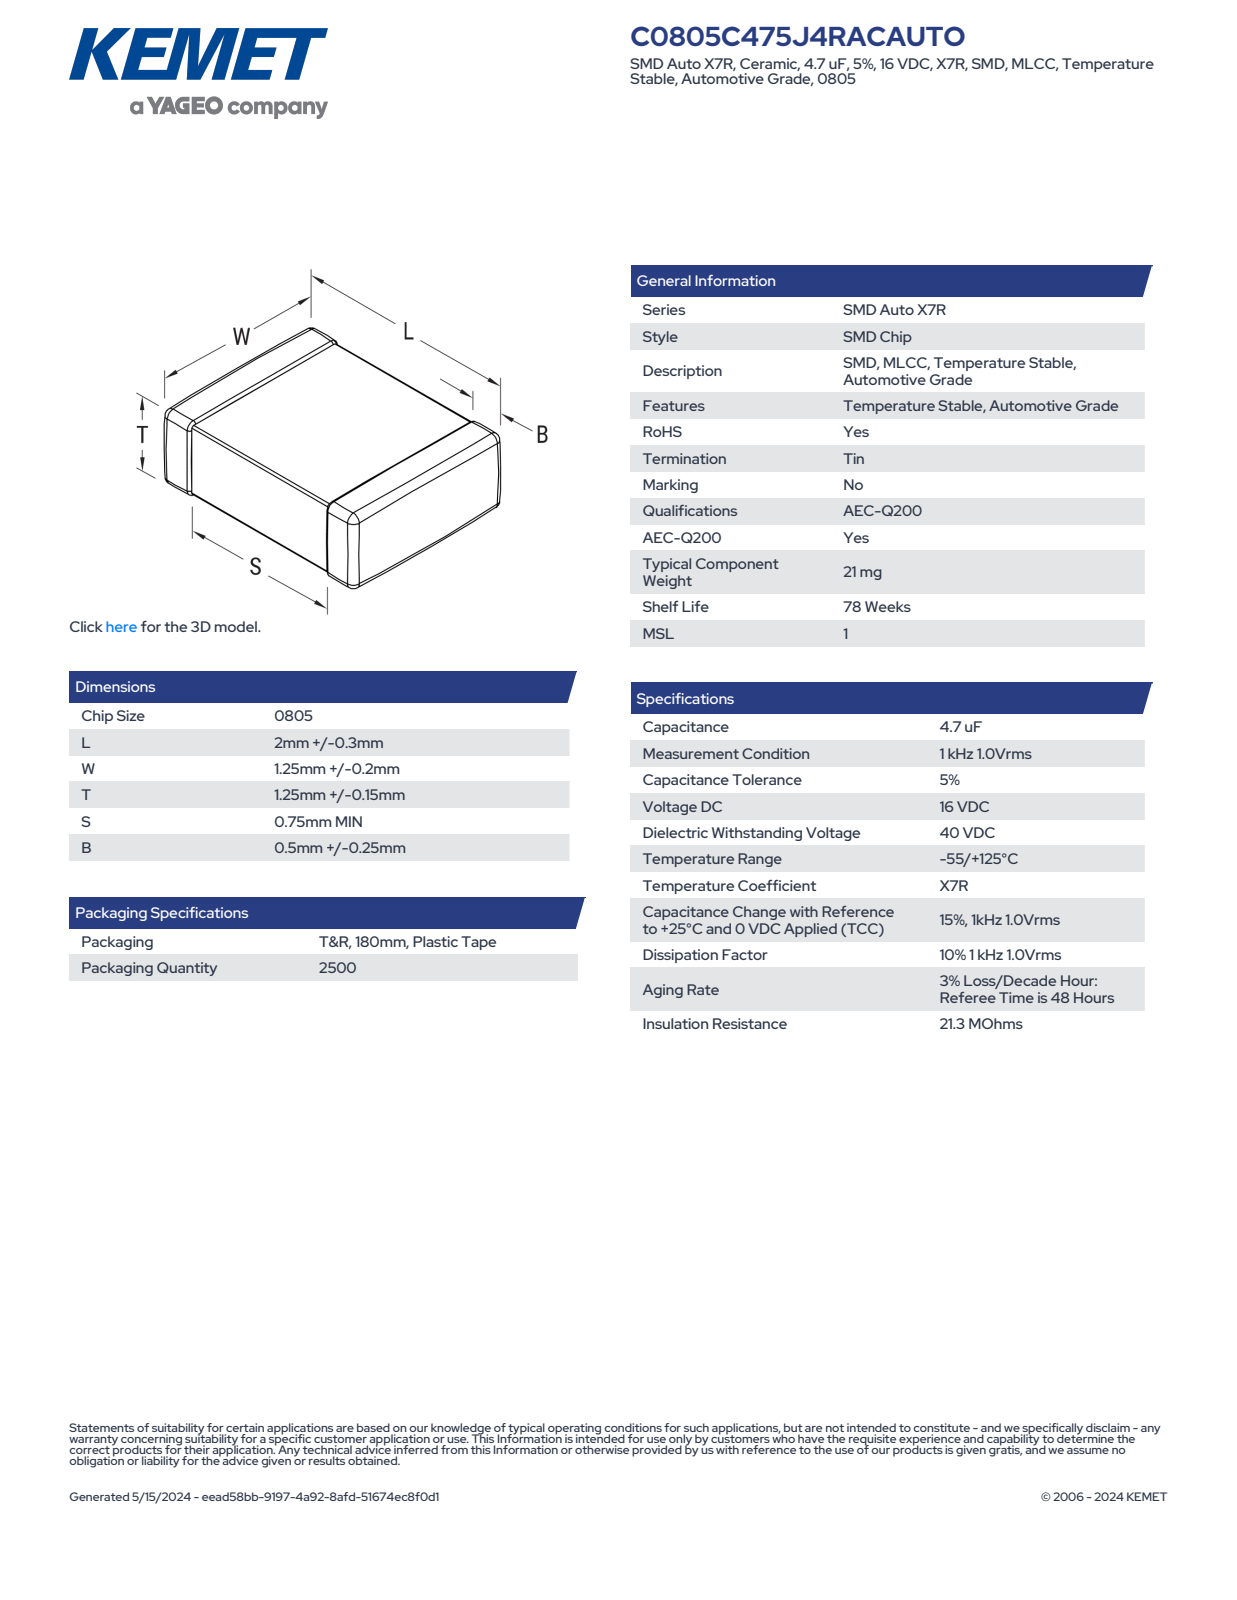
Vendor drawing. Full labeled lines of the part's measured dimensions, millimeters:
Part name (STEP PRODUCT): CCS_CCSTD_0805_L2.3W1.45T1.4B0.5
STEP written by: SolidWorks 2021 (AUTOMOTIVE_DESIGN)
Units: millimetres
Bodies: 4 solids, 125 faces (71 planar, 38 cylindrical, 16 other)
Overall size (bounding box): 2.3 × 1.45 × 1.4
Volume: 5 mm³ · Surface area: 17 mm²
Main face-to-face distances: 1.37, 1.42, 1.4, 2.3, 1.45, 1.34, 1.39, 1.03, 1.27, 1.24
